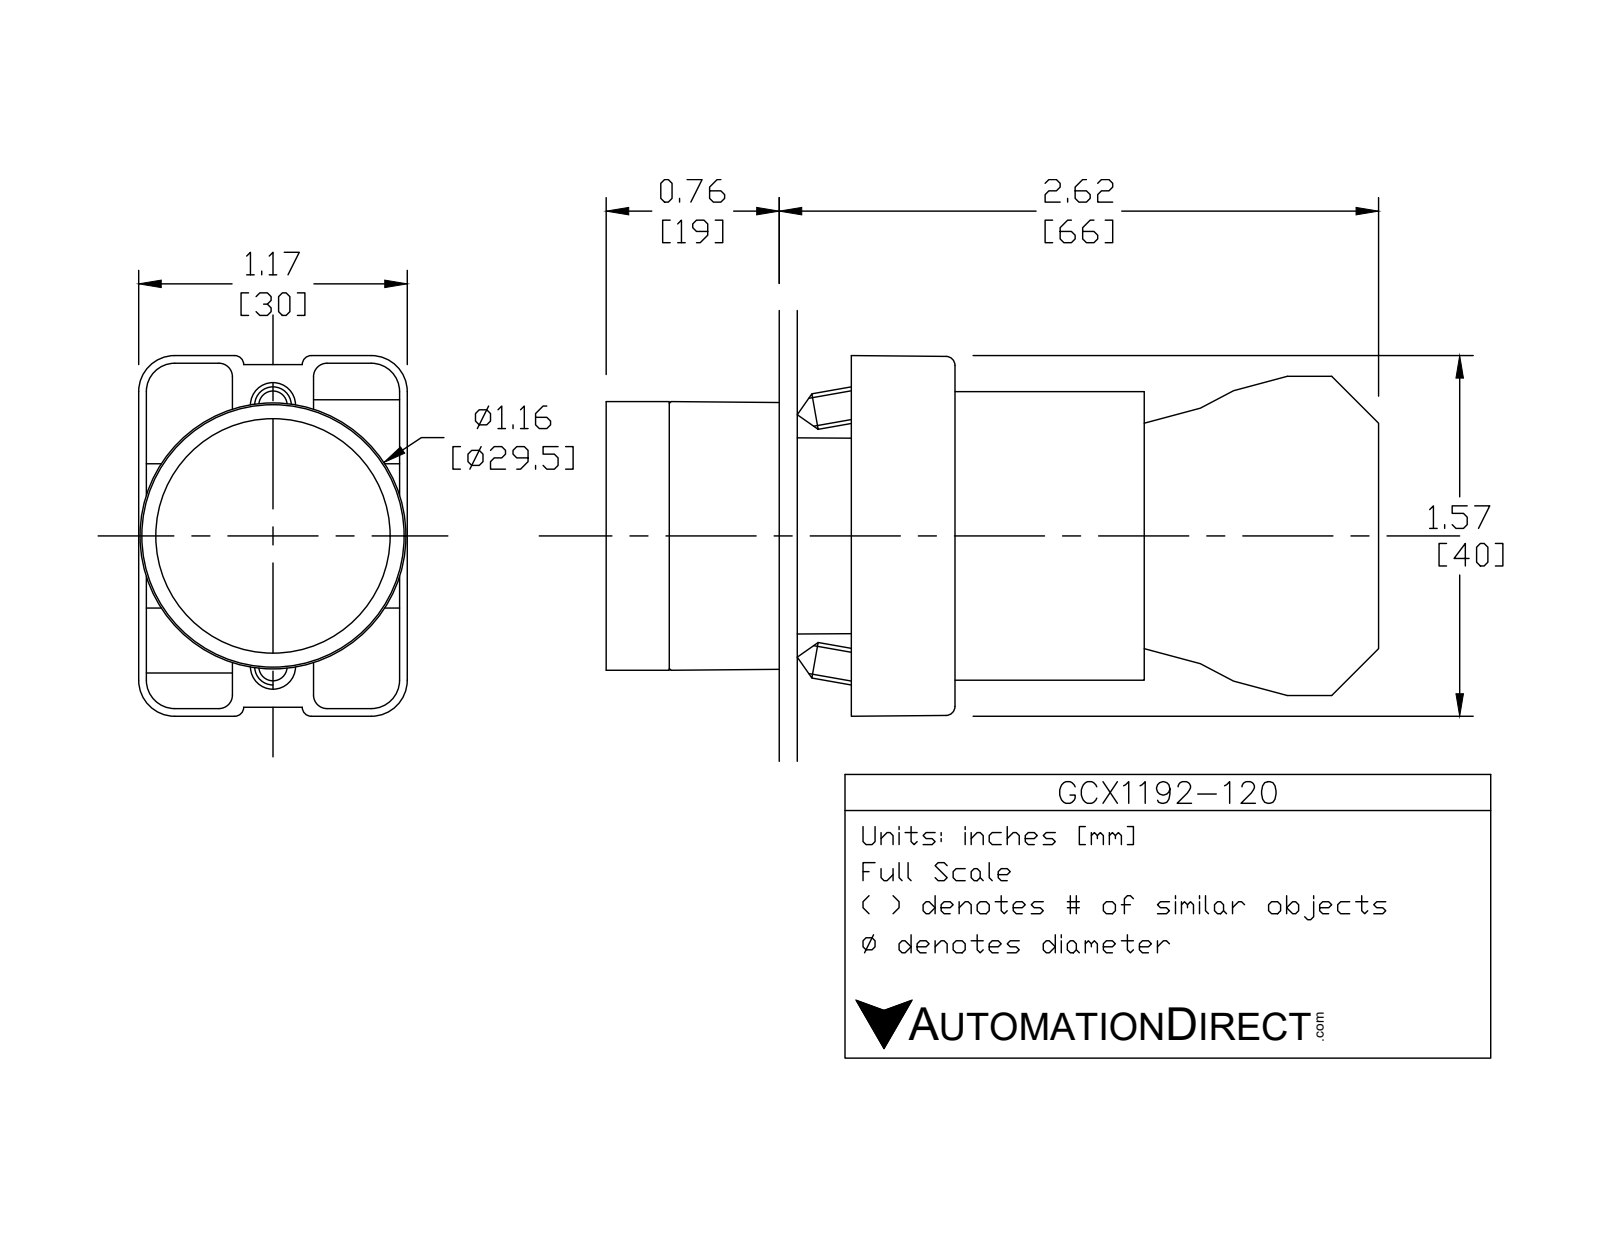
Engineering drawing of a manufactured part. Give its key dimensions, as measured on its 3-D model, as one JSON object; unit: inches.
{"part_name": "ecx1029; GCX1192-120; ecx1040; ECX1050 (+1 more)", "step_written_by": "SolidWorks 2016 (AUTOMOTIVE_DESIGN)", "units": "inches", "bodies": {"solids": 8, "faces": 431, "planar": 252, "cylindrical": 148, "other": 31}, "overall_size": [3.319, 1.581, 1.177], "volume_in3": 2.794, "surface_area_in2": 38.75, "round_holes": [[0.079, 2], [0.124, 2], [0.13, 2], [0.087, 1], [0.197, 1], [0.469, 1], [0.878, 1], [0.888, 1], [1.024, 1]], "round_bosses_or_shafts": [[0.157, 4], [1.175, 1], [1.004, 1], [0.945, 1], [0.856, 1], [0.78, 1], [0.504, 1]], "partial_cylinders_radius": [[0.059, 24], [0.041, 12], [0.124, 12], [0.157, 12], [0.039, 8], [0.128, 2], [0.02, 1], [0.063, 1]], "face_to_face_distances": [0.827, 2.02, 1.193, 0.579, 1.171, 0.031, 0.276, 0.033, 0.748, 0.573], "hole_center_spacings": [0.236, 0.544, 0.472, 0.49]}
